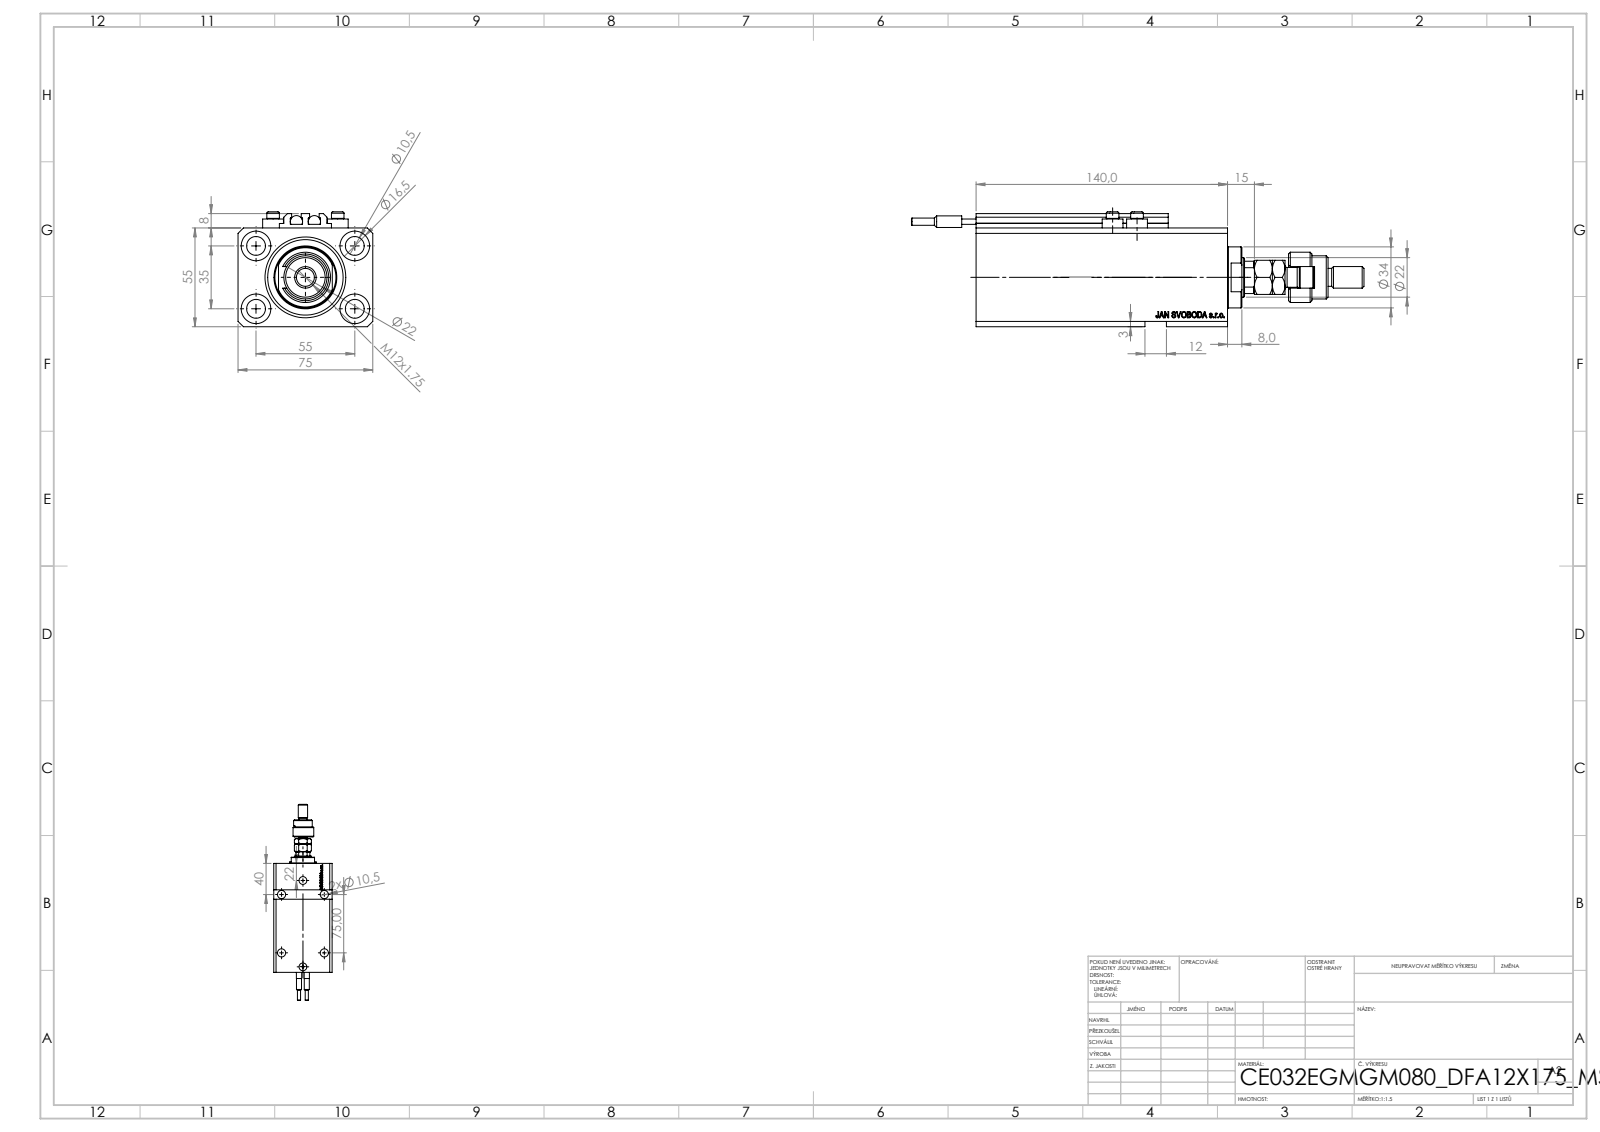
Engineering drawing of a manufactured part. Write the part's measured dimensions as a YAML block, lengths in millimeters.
part_name: "V250CE_E_Body; V250CE_C_VCP; FEMALE_PART_FOR_DFA; ALLEN BOLT V250CE (+3 more)"
step_written_by: "SolidWorks 2019 (CONFIG_CONTROL_DESIGN)"
units: millimeters
bodies: {solids: 12, faces: 1221, planar: 574, cylindrical: 171, other: 476}
overall_size: [252, 75, 64]
volume: 506672
surface_area: 125175
round_holes:
  - {diameter: 10.5, count: 9}
  - {diameter: 1.25, count: 4}
  - {diameter: 4, count: 4}
  - {diameter: 16.5, count: 4}
  - {diameter: 10, count: 2}
  - {diameter: 13.16, count: 2}
  - {diameter: 20, count: 2}
  - {diameter: 22, count: 1}
  - {diameter: 32, count: 1}
  - {diameter: 45, count: 1}
round_bosses_or_shafts:
  - {diameter: 11.6, count: 4}
  - {diameter: 7, count: 4}
  - {diameter: 6.8, count: 2}
  - {diameter: 6.5, count: 2}
  - {diameter: 4, count: 2}
  - {diameter: 34, count: 1}
  - {diameter: 28, count: 1}
  - {diameter: 24, count: 1}
partial_cylinders:
  - {radius: 0.2, count: 10}
  - {radius: 9.75, count: 1}
  - {radius: 10.5, count: 1}
face_to_face_distances: [55, 75, 15, 3, 57, 140, 8, 125, 9.9, 2]
hole_center_spacings: [32.6, 32.87, 55, 96.98, 13.6, 14.09, 25.81, 32.58]
